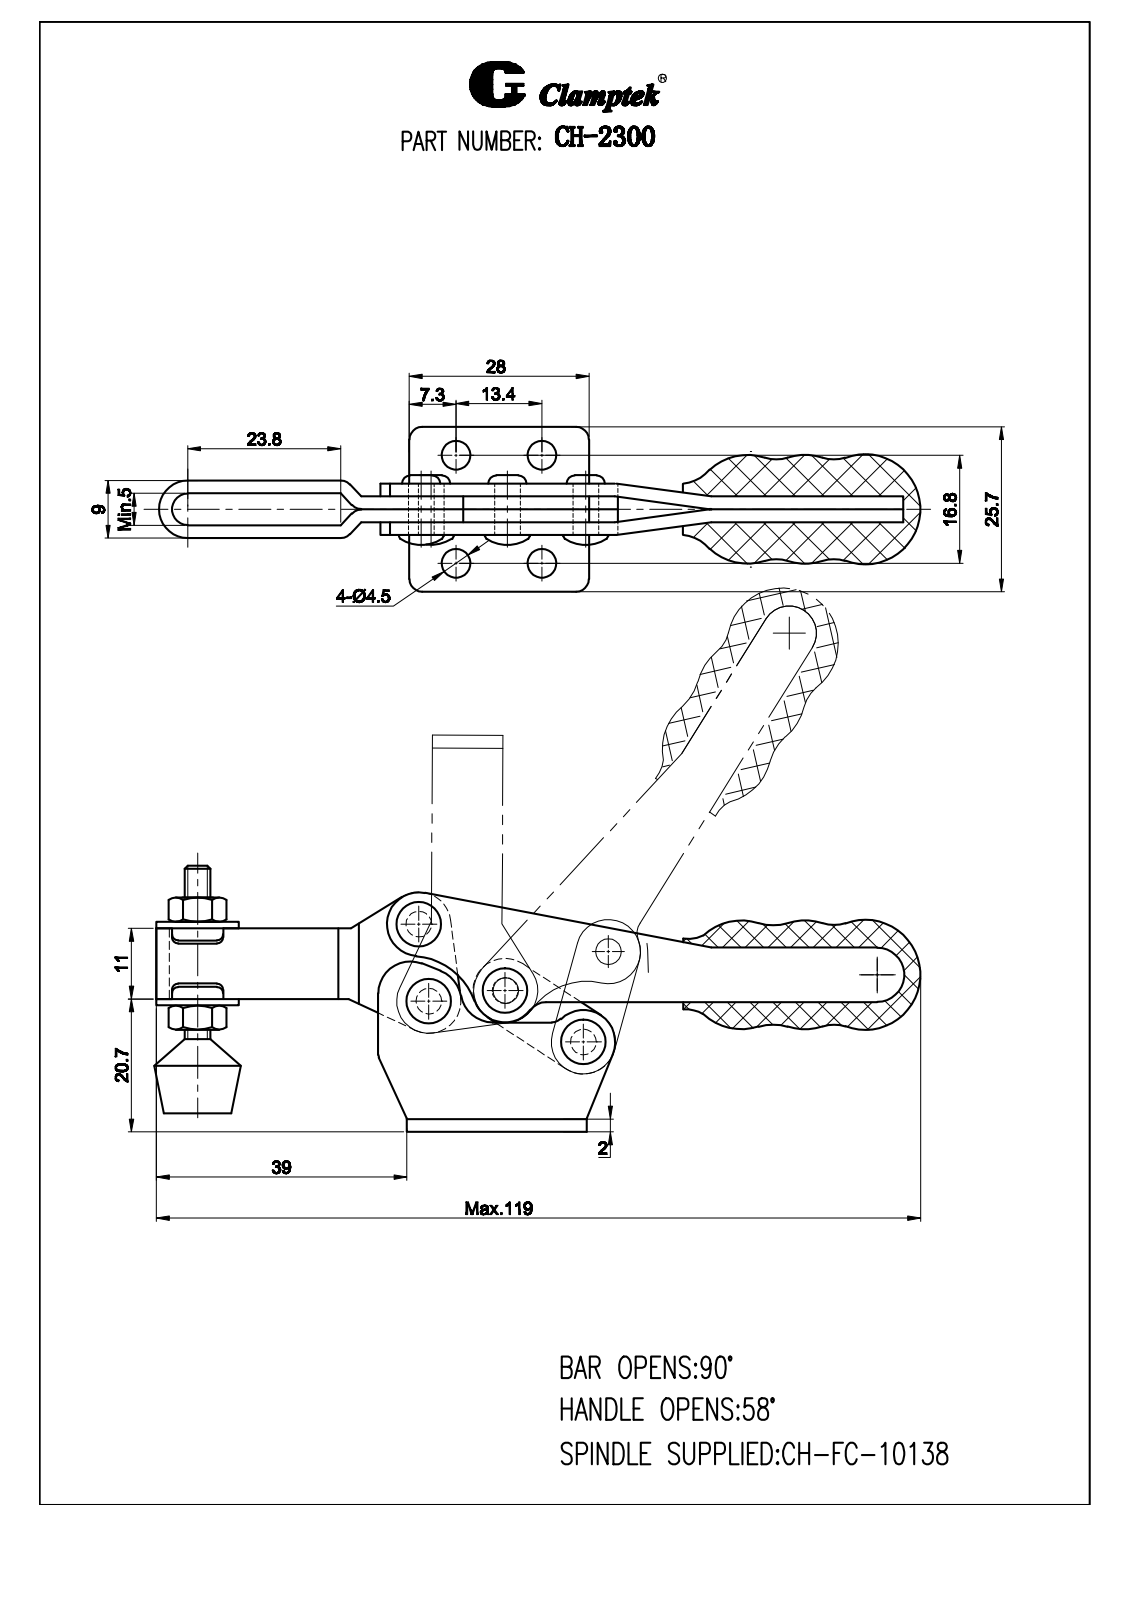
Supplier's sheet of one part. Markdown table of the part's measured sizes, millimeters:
| quantity | value |
| --- | --- |
| part name | CH-2300-01; CH-2300-05; FW100; CH-2300 (+6 more) |
| STEP written by | SolidWorks 2010 (CONFIG_CONTROL_DESIGN) |
| units | millimeters |
| bodies | 16 solids, 731 faces (251 planar, 190 cylindrical, 290 other) |
| overall size | 134.97 × 40.98 × 25.6 |
| volume | 17 574 mm³ |
| surface area | 17 580 mm² |
| round holes (diameter × count) | 2.9 × 4, 4 × 4, 4.5 × 4, 3.8 × 2, 3.98 × 2, 4.9 × 2, 2.4 × 1, 9.53 × 1 |
| round bosses / shafts (diameter × count) | 7 × 4, 6.4 × 4, 3.9 × 4, 15.32 × 1, 4.8 × 1, 1.6 × 1 |
| partial cylindrical surfaces (radius × count) | 2 × 12, 5 × 5, 1 × 4, 6.3 × 2, 2.5 × 1, 2.69 × 1, 3 × 1, 4.19 × 1 |
| main face-to-face distances | 2, 4, 6, 8, 0.5, 2.5, 4.5, 6.5, 8.5, 1.5 |
| hole center spacings | 13.4, 16.8, 21.49, 12.12, 13.37, 14.6, 17.09, 24.94 |
